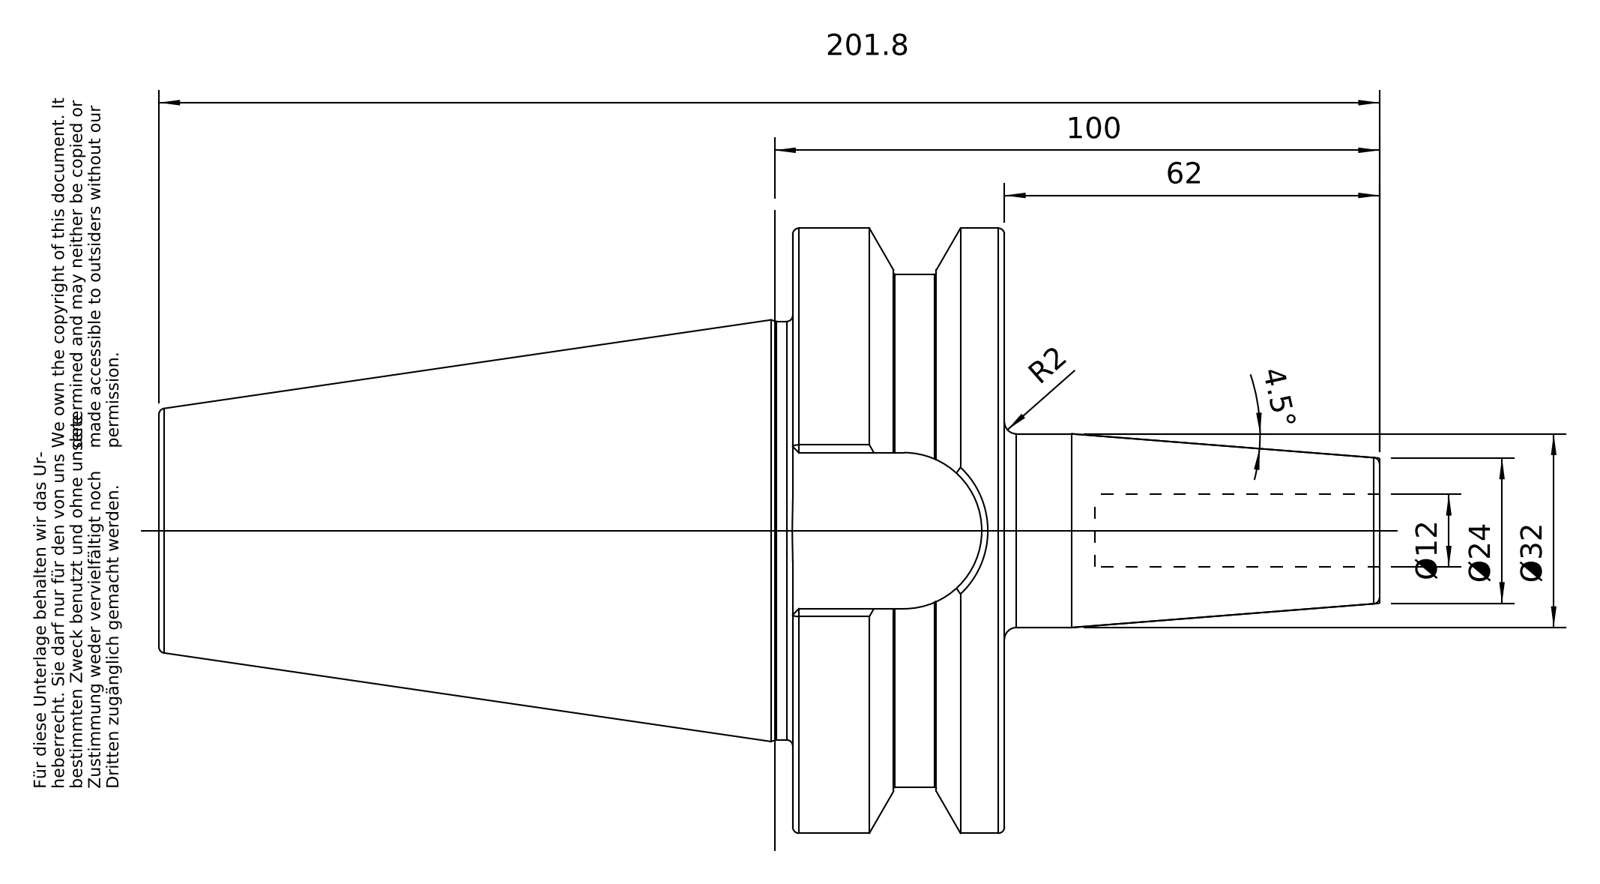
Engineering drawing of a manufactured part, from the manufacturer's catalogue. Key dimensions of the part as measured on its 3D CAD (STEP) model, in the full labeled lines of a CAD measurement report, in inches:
Part name (STEP PRODUCT): 50-640-12
STEP written by: PRO/ENGINEER BY PARAMETRIC TECHNOLOGY CORPORATION, 2010430 (CONFIG_CONTROL_DESIGN)
Units: inches
Bodies: 1 solid, 96 faces (26 planar, 22 cylindrical, 48 other)
Overall size (bounding box): 7.945 × 3.936 × 3.936
Volume: 30.71 in³ · Surface area: 91.08 in²
Round holes (diameter × count): ⌀0.472 ×1, ⌀0.817 ×1, ⌀0.985 ×1, ⌀1.012 ×1
Round bosses / shafts (diameter × count): ⌀3.936 ×1, ⌀3.337 ×1, ⌀2.722 ×1, ⌀1.26 ×1, ⌀0.945 ×1
Partial cylindrical surfaces — rounded edges, fillets, slot ends (radius × count): R0.508 ×1
Main face-to-face distances: 1.378, 2.772, 4.126, 5.504, 1.016, 7.945, 3.819, 2.441, 1.89, 2.236
